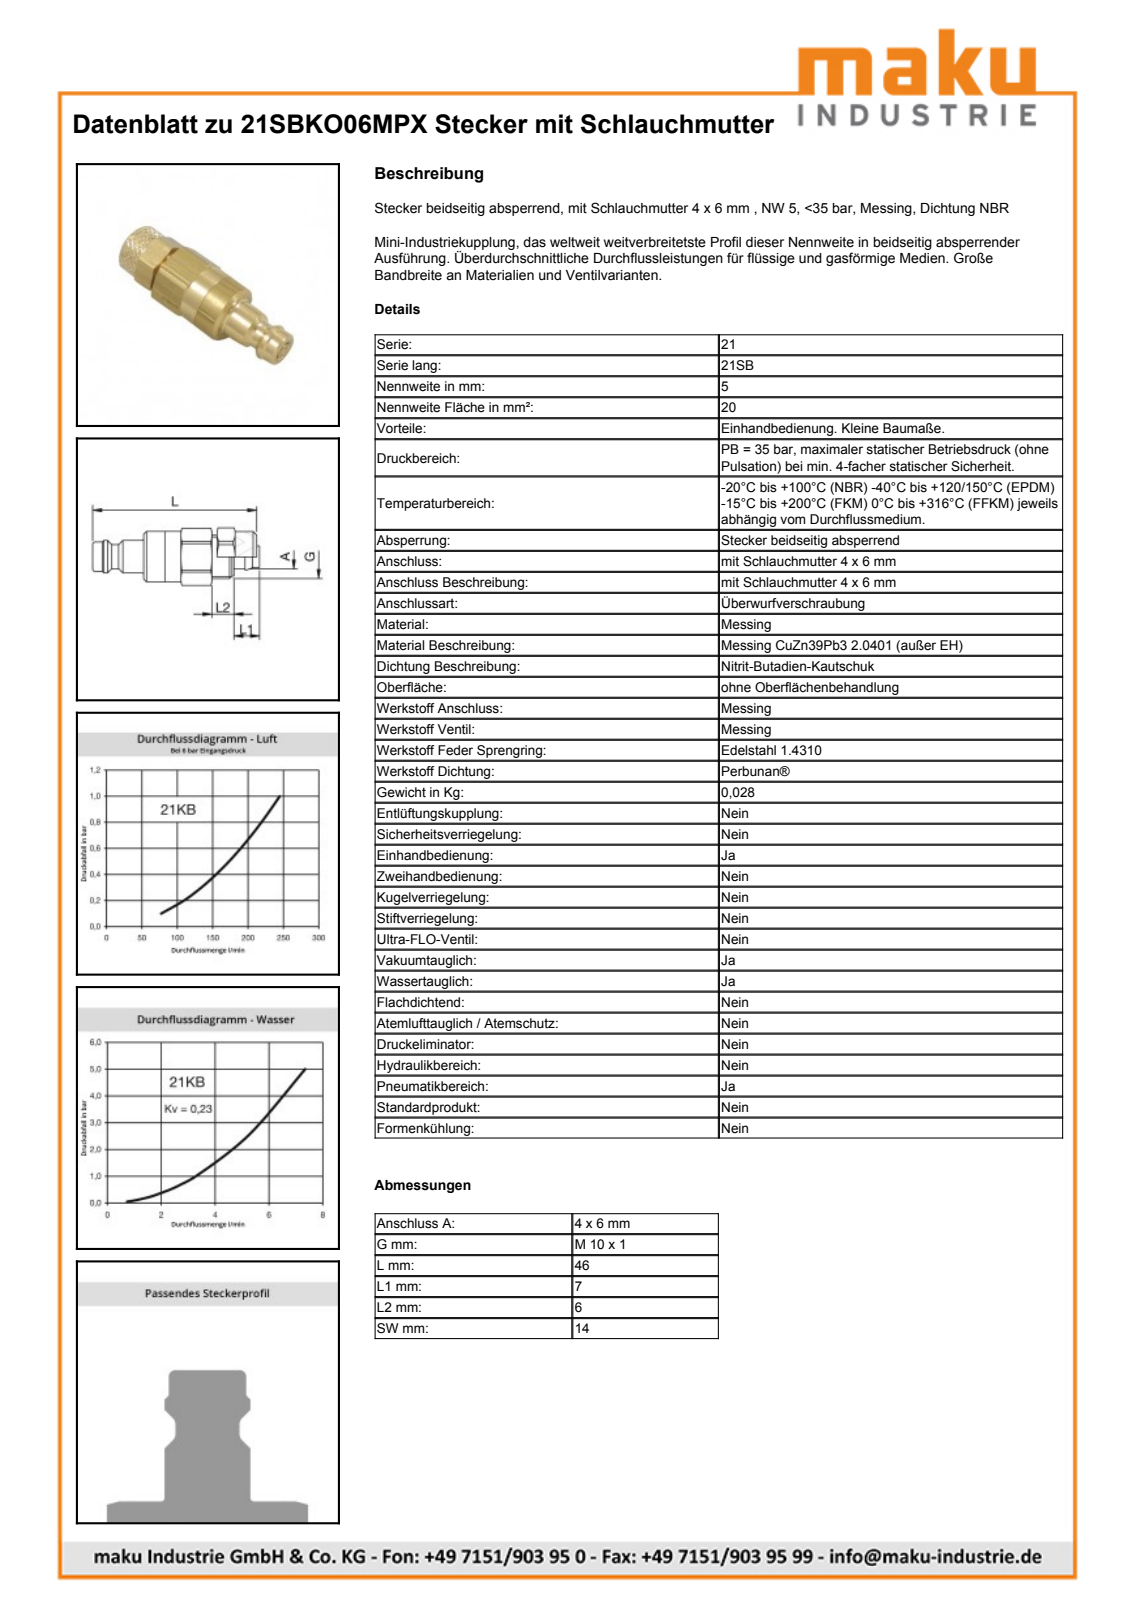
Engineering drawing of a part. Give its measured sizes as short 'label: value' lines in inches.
name: D105884
written by: Autodesk Inventor 2013 (AUTOMOTIVE_DESIGN)
unit: in
bodies: 1 solid, 97 faces (22 planar, 28 cylindrical, 47 other)
size: 1.805 × 0.612 × 0.601
volume: 0.299 in³; area: 4.382 in²
holes: 1× ⌀0.244, 1× ⌀0.351, 1× ⌀0.472
bosses: 1× ⌀0.551, 1× ⌀0.472, 1× ⌀0.435, 1× ⌀0.394, 1× ⌀0.354, 1× ⌀0.339, 1× ⌀0.319, 1× ⌀0.262
rounds: 1× R0.266, 1× R0.311
face distances: 0.551, 0.472, 0.476, 0.734, 1.211, 0.555, 1.289, 1.766, 1.53, 0.974
